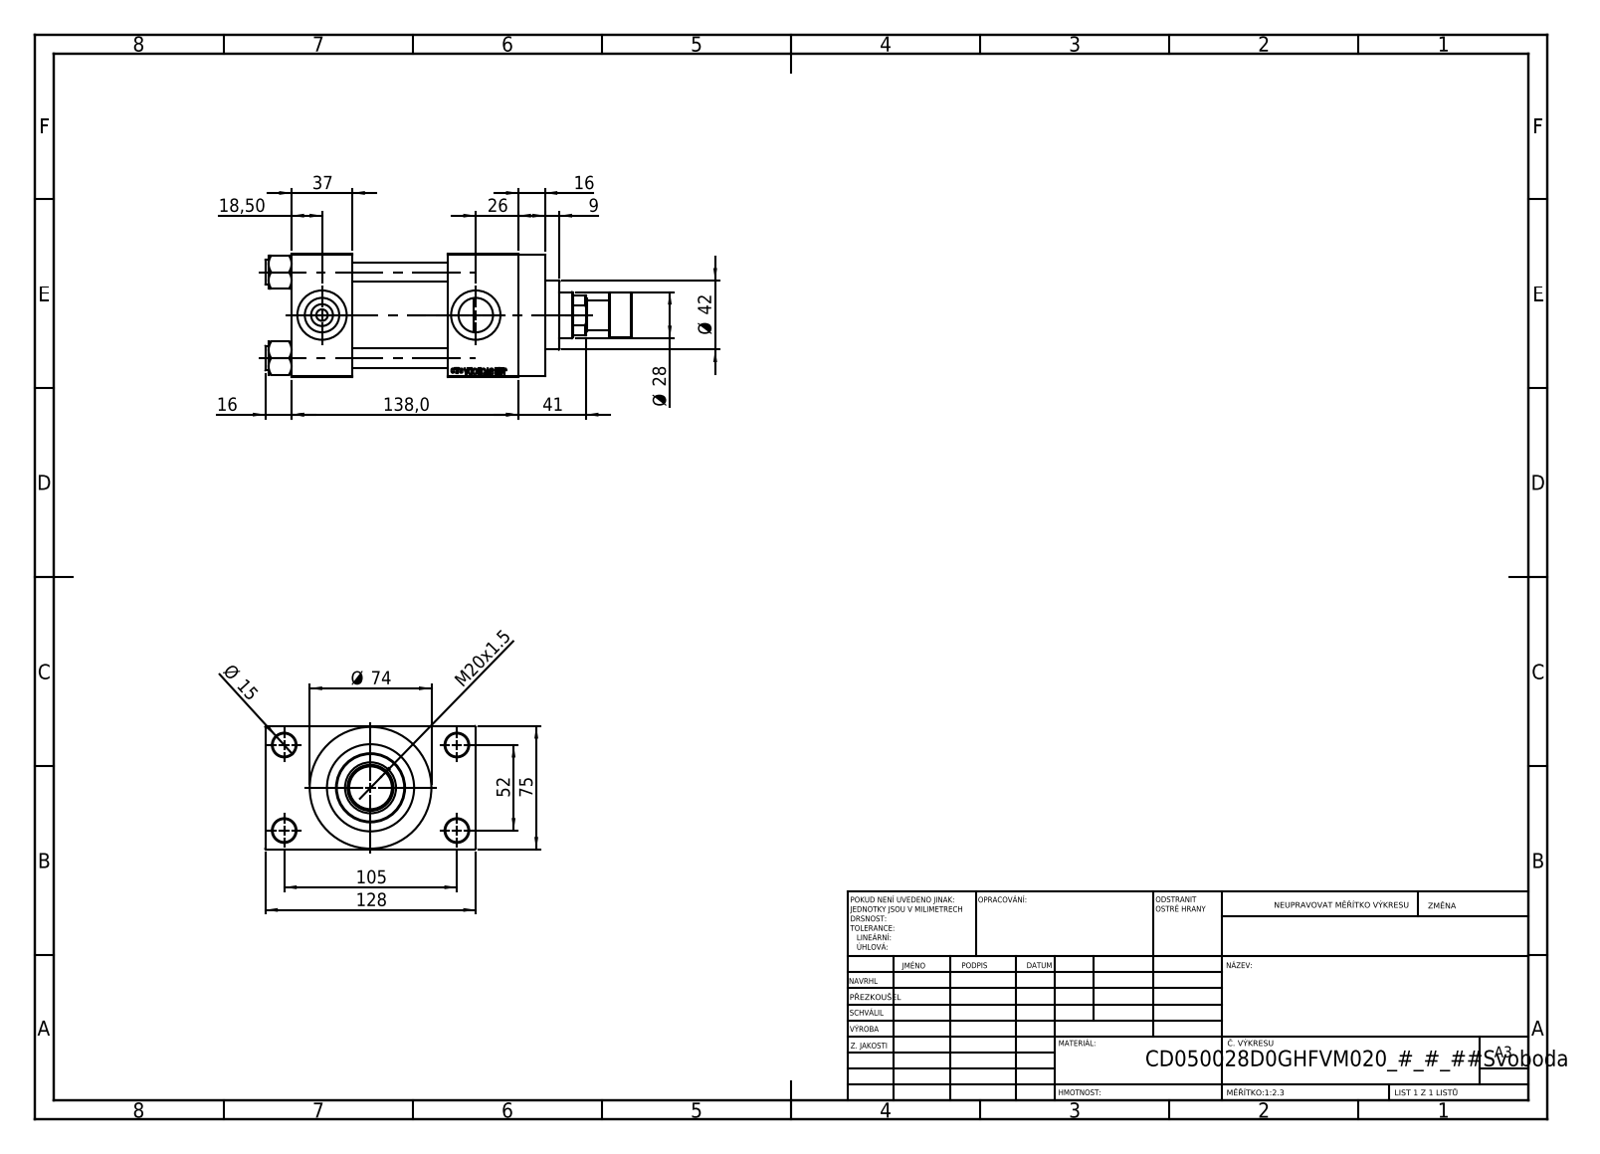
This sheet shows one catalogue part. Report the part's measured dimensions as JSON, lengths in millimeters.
{"part_name": "V215CD_D_Body; V215CD_NUT_M5_D; V215CR_ROD_END_F; V215CD_VC_A (+2 more)", "step_written_by": "SolidWorks 2019 (CONFIG_CONTROL_DESIGN)", "units": "millimeters", "bodies": {"solids": 12, "faces": 1117, "planar": 501, "cylindrical": 92, "other": 524}, "overall_size": [223, 128, 75], "volume_mm3": 817817, "surface_area_mm2": 173865, "round_holes": [[12, 4], [14, 4], [7, 2], [20.96, 2], [30, 2], [18.5, 1], [28, 1], [31, 1], [41, 1], [50, 1], [53, 1]], "round_bosses_or_shafts": [[15, 4], [74, 1], [56, 1], [42, 1], [27, 1], [18, 1]], "face_to_face_distances": [75, 58, 37, 95, 26.5, 138, 101, 43, 101.5, 16], "hole_center_spacings": [26.35, 36.98, 52.3, 58.43, 58.59, 78.65, 94.37, 52]}
